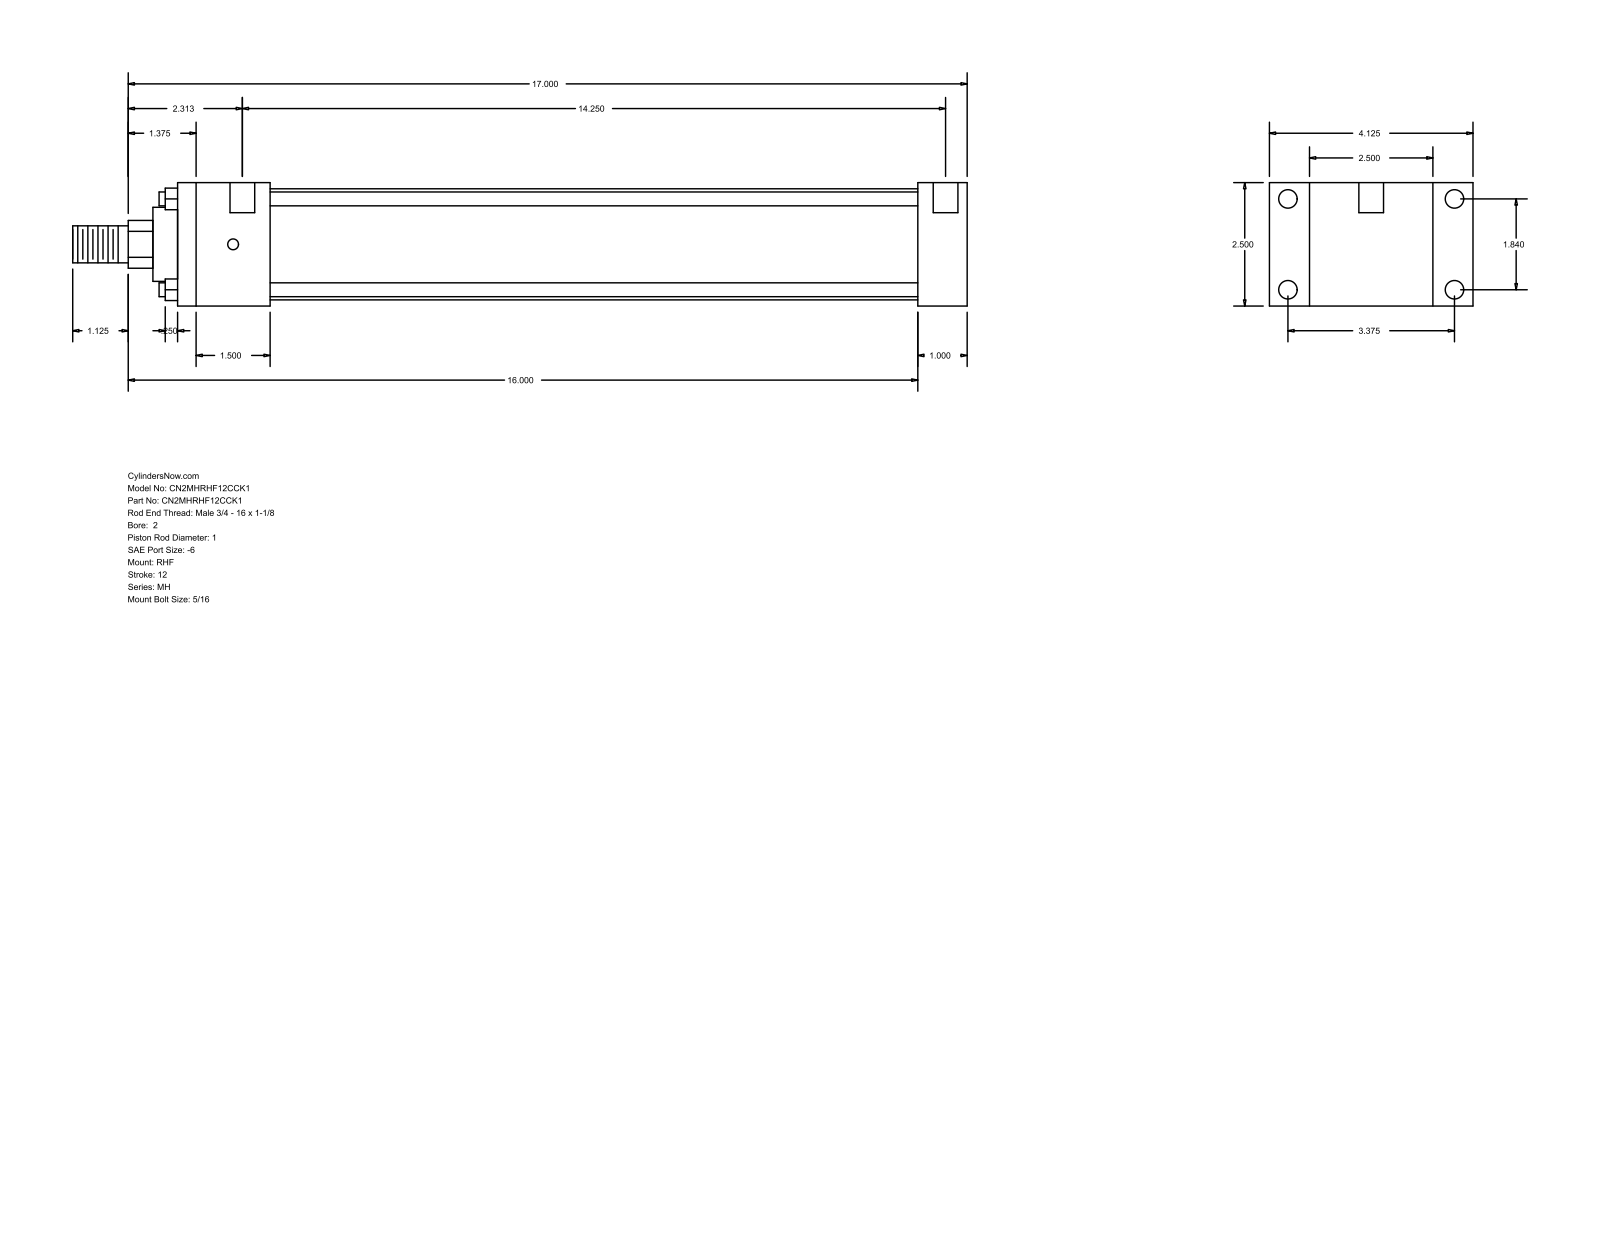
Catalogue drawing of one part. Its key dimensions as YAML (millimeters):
part_name: "MH_RHF__0200_1"
step_written_by: "GSSL Pune (CONFIG_CONTROL_DESIGN)"
units: millimeters
bodies: {solids: 0, faces: 88, planar: 60, cylindrical: 28, other: 0}
overall_size: [460.38, 104.78, 63.5]
round_holes:
  - {diameter: 5.56, count: 4}
  - {diameter: 9.53, count: 4}
  - {diameter: 12.7, count: 2}
round_bosses_or_shafts:
  - {diameter: 7.14, count: 4}
  - {diameter: 57.15, count: 1}
  - {diameter: 38.1, count: 1}
  - {diameter: 25.4, count: 1}
  - {diameter: 19.05, count: 1}
partial_cylinders:
  - {radius: 12.29, count: 1}
face_to_face_distances: [63.5, 25.4, 20.64, 84.14, 406.4, 381, 104.78, 47.63, 333.37, 358.77]
hole_center_spacings: [46.74, 85.72, 97.63, 369.88, 3.17, 4.76, 361.95, 365.12]
